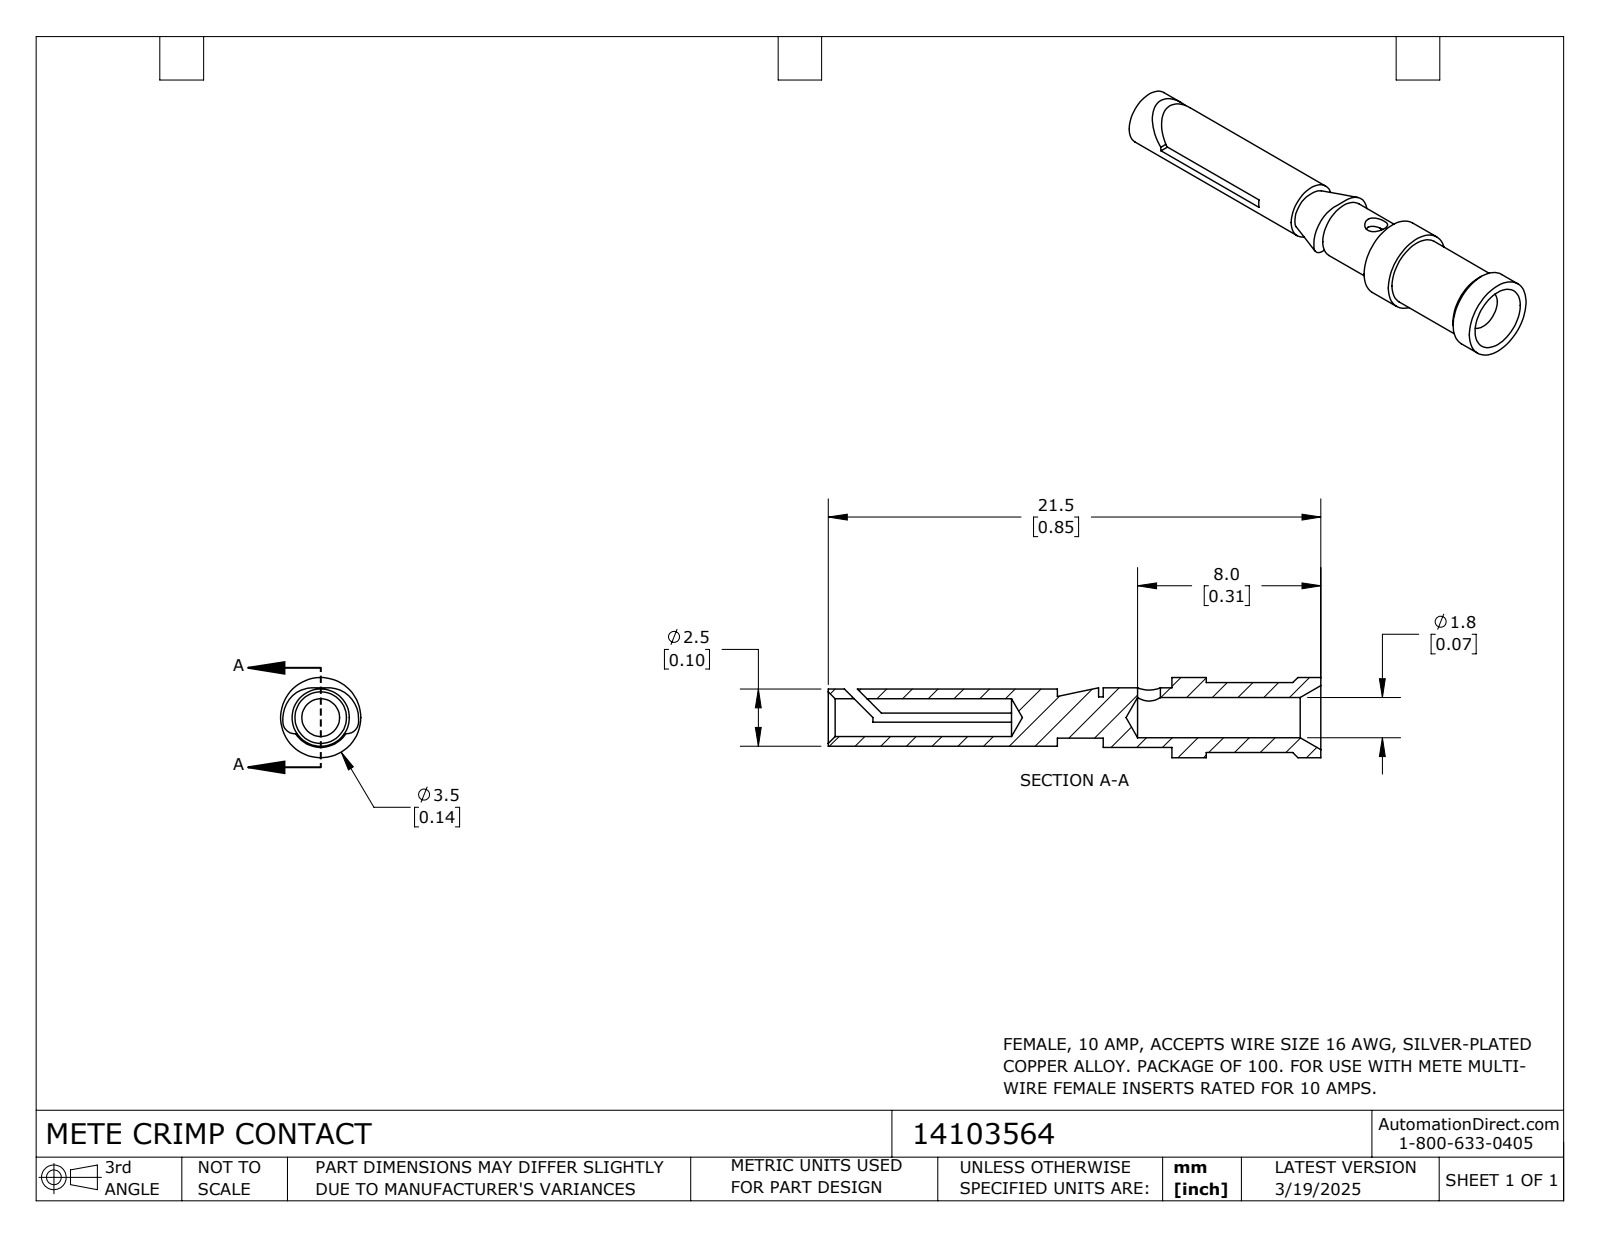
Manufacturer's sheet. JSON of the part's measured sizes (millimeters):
{"part_name": "14103564", "step_written_by": "SolidWorks 2024 (CONFIG_CONTROL_DESIGN)", "units": "millimeters", "bodies": {"solids": 1, "faces": 48, "planar": 17, "cylindrical": 20, "other": 11}, "overall_size": [21.5, 3.5, 3.5], "volume_mm3": 85, "surface_area_mm2": 300, "round_holes": [[1, 1], [1.65, 1], [1.75, 1]], "round_bosses_or_shafts": [[3.5, 1], [3.05, 1], [2.6, 1], [2.5, 1], [1.8, 1]], "face_to_face_distances": [0.4, 6.5, 5, 9.7, 3.2, 9.5, 3, 2, 1.5, 4.5]}
